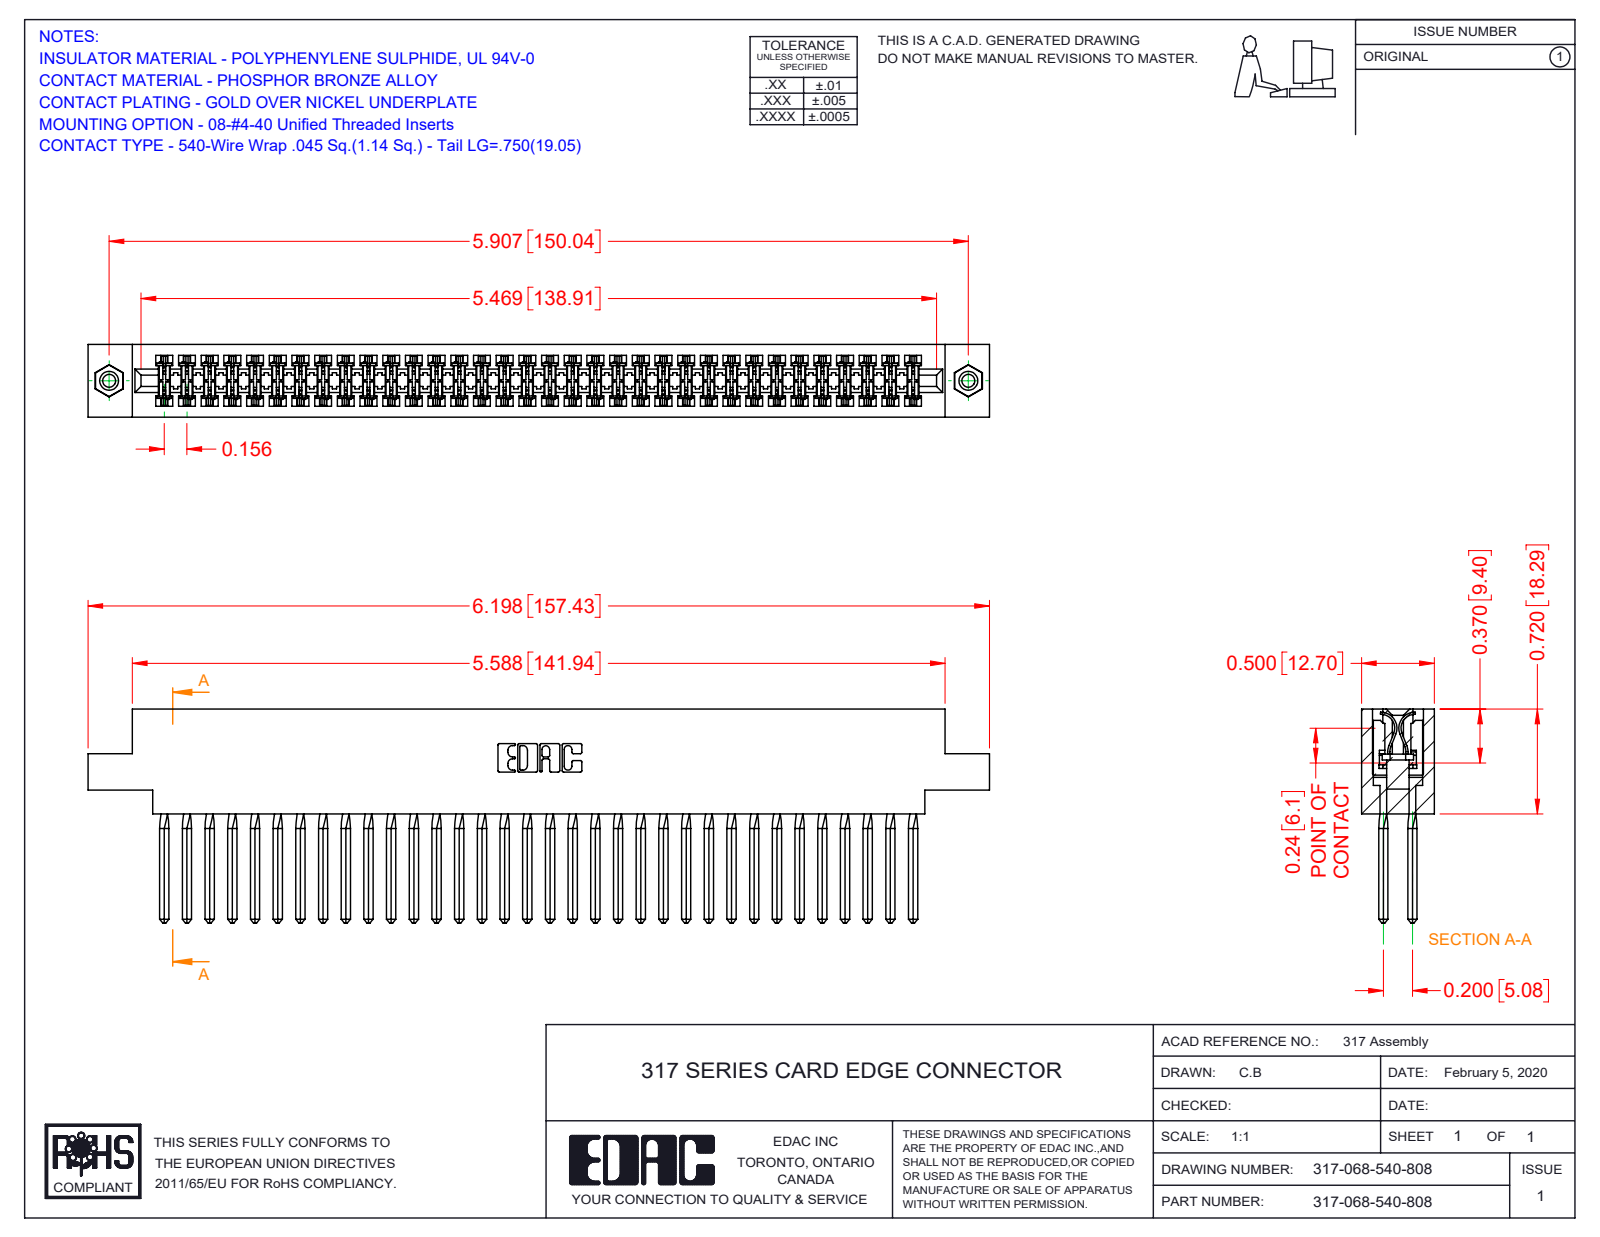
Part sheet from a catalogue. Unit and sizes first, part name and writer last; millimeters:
Units: millimetres
Overall size (bounding box): 157.4 × 37.3 × 12.7
Round holes (diameter × count): ⌀2.3 ×2, ⌀3.2 ×2, ⌀4 ×2
Round bosses / shafts (diameter × count): ⌀3.9 ×2
Partial cylindrical surfaces — rounded edges, fillets, slot ends (radius × count): R0.4 ×136, R0.3 ×22, R0.2 ×6, R0.8 ×6, R0.7 ×3, R2.4 ×2, R2.5 ×2, R2.8 ×2
Main face-to-face distances: 12.7, 1.9, 10.8, 8.9, 5, 2.8, 2.4, 5.1, 2.9, 3.3
Hole centre spacings: 150
Volume: 26 140 mm³ · Surface area: 38 700 mm²
Bodies: 71 solids, 6214 faces (5054 planar, 872 cylindrical, 288 other)
Part name (STEP PRODUCT): 317-290-001_540; 345-250-001_345-250-003-102; 317 Part_.156 Dia - TI; 317-068-540-878
STEP written by: SolidWorks 2016 (CONFIG_CONTROL_DESIGN)
